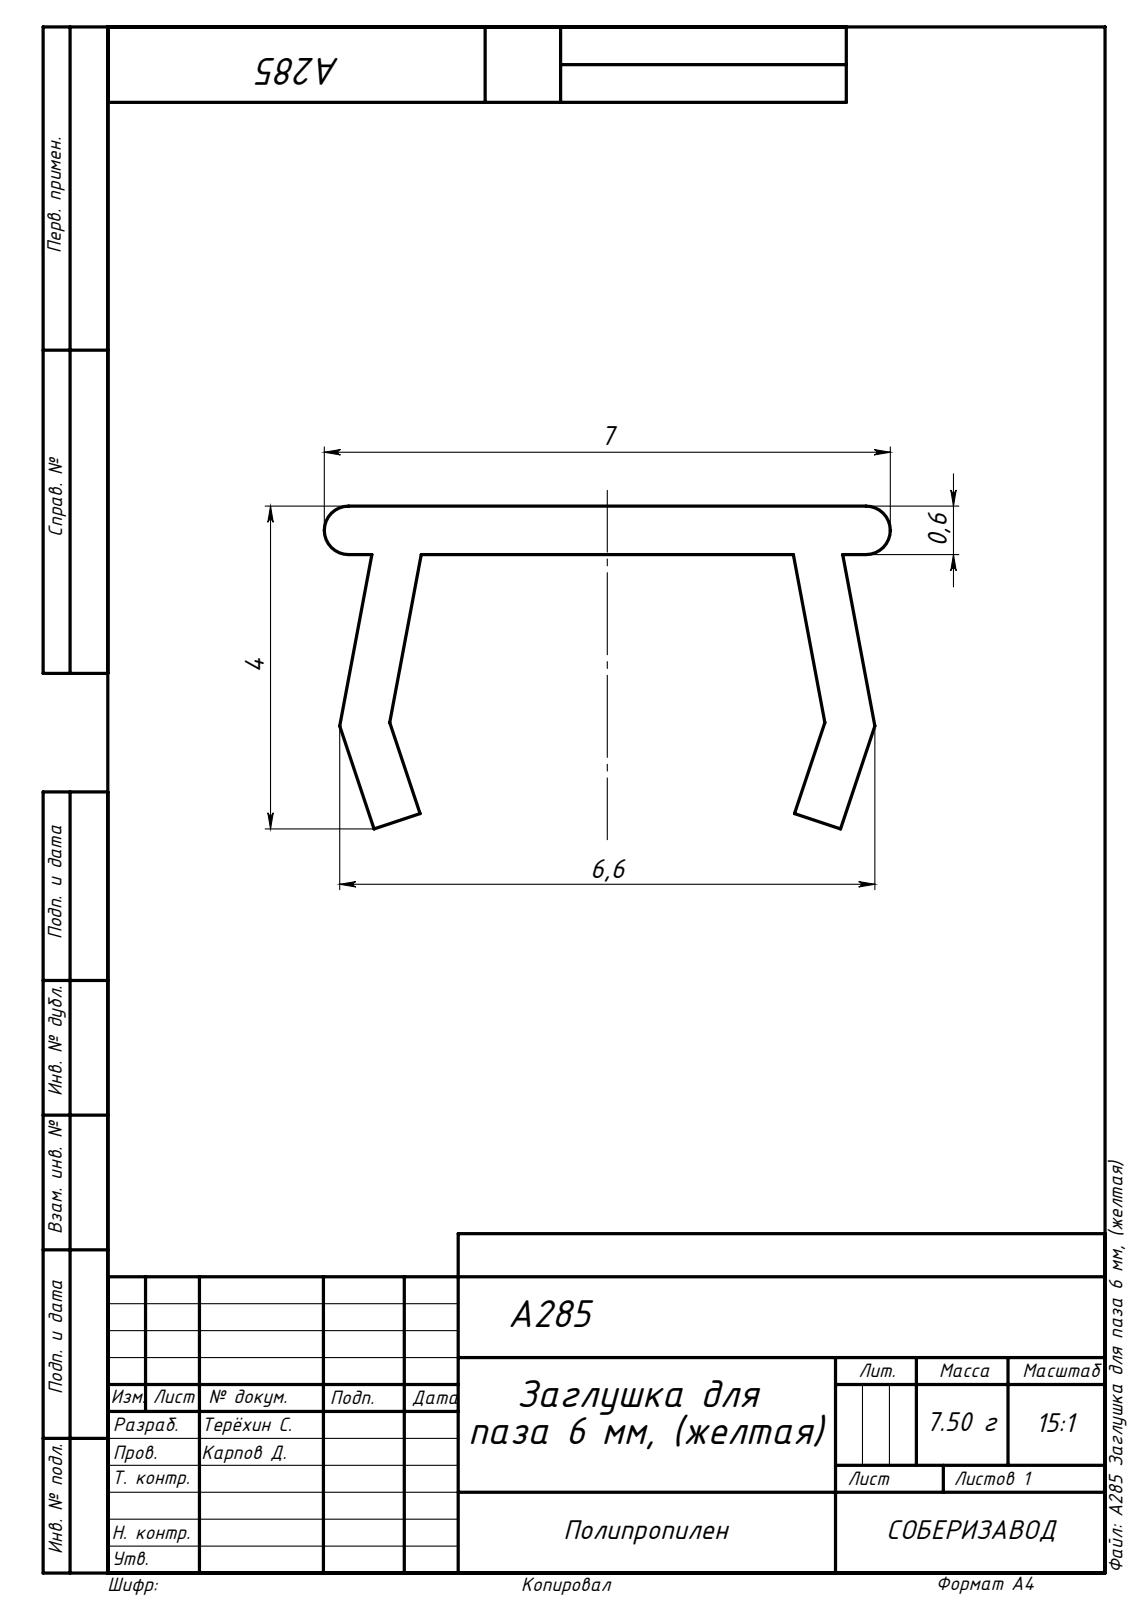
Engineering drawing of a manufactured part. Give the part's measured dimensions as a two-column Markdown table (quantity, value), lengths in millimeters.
| quantity | value |
| --- | --- |
| part name | A285 Заглушка для паза 6 мм, (желтая) |
| STEP written by | SolidWorks 2019 (AUTOMOTIVE_DESIGN) |
| units | millimeters |
| bodies | 1 solid, 20 faces (16 planar, 4 cylindrical, 0 other) |
| overall size | 1000 × 7 × 4 |
| volume | 8 205 mm³ |
| surface area | 28 286 mm² |
| partial cylindrical surfaces (radius × count) | 0.3 × 2 |
| main face-to-face distances | 0.6, 0.61, 1000 |
